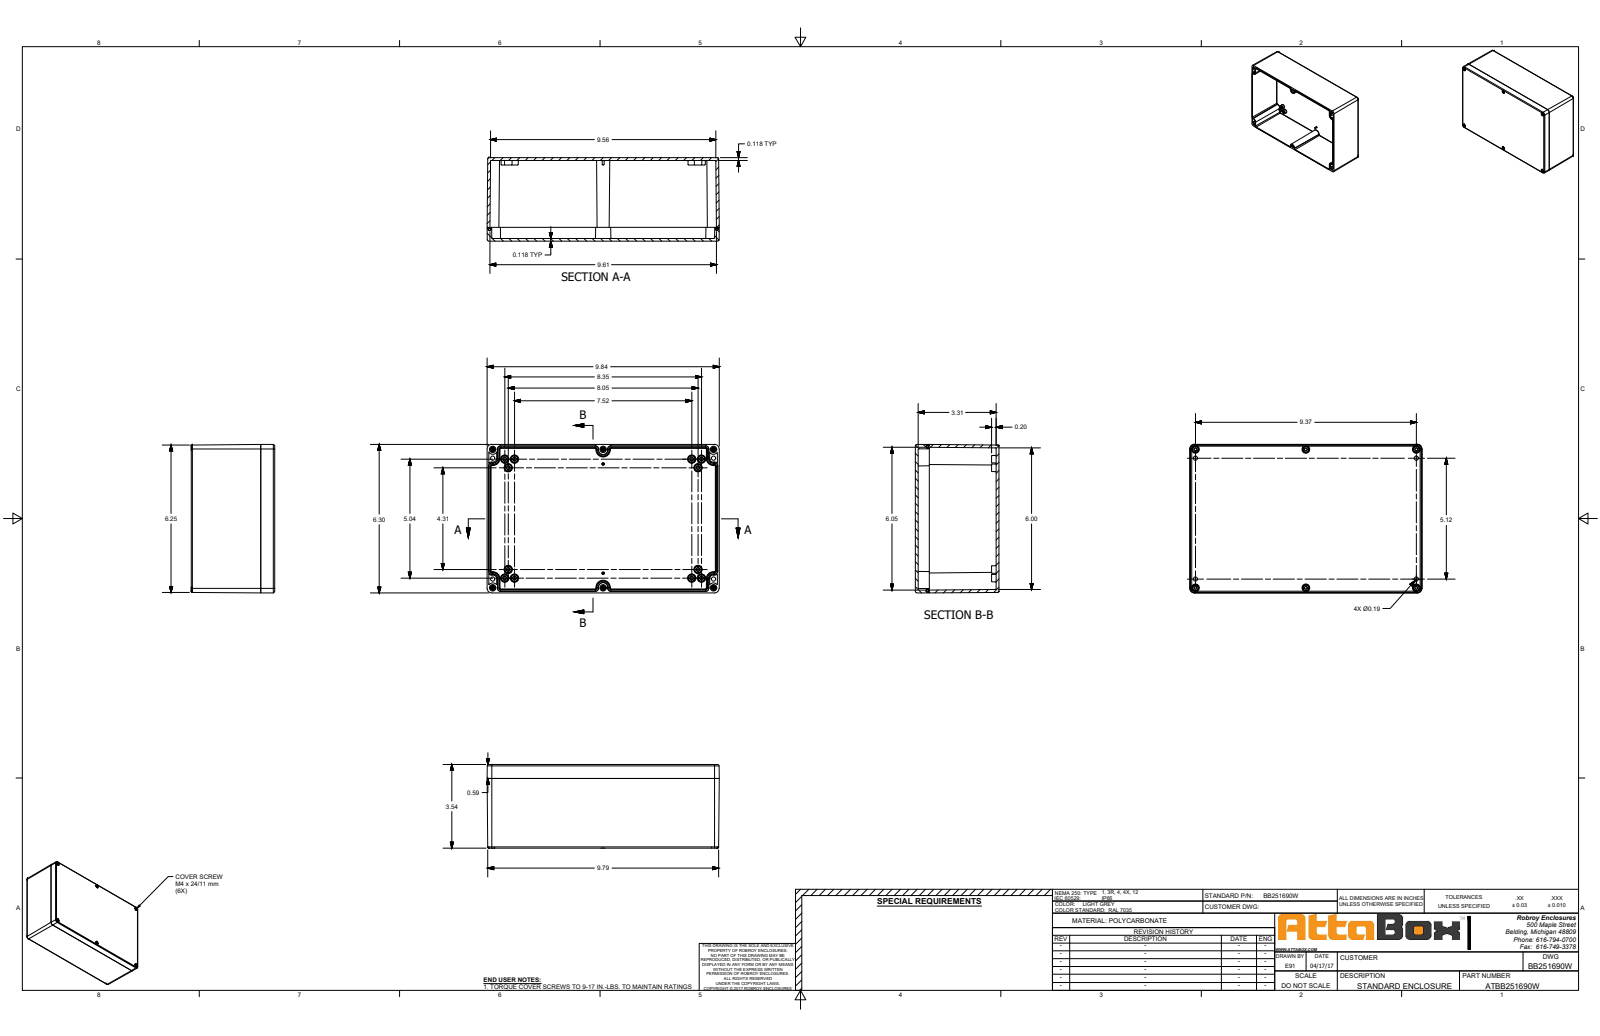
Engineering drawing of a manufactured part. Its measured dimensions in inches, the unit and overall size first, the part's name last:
Units: inches
Overall size (bounding box): 9.843 × 6.299 × 3.544
Round holes (diameter × count): ⌀0.128 ×6, ⌀0.177 ×6, ⌀0.193 ×6, ⌀0.201 ×6, ⌀0.276 ×6, ⌀0.291 ×6, ⌀0.323 ×6, ⌀0.185 ×4
Round bosses / shafts (diameter × count): ⌀0.268 ×6, ⌀0.173 ×6, ⌀0.157 ×6, ⌀0.13 ×6
Partial cylindrical surfaces — rounded edges, fillets, slot ends (radius × count): R0.049 ×40, R0.02 ×32, R0.039 ×20, R0.059 ×16, R0.167 ×16, R0.004 ×12, R0.102 ×6, R0.124 ×6
Main face-to-face distances: 0.118, 3.425, 3.543, 3.307, 0.124, 6.175, 6.299, 6.112, 0.187, 5.988
Hole centre spacings: 0.374, 4.685, 4.7, 5.492, 7.219, 7.507, 9.37, 9.378
Volume: 30.25 in³ · Surface area: 532.6 in²
Bodies: 15 solids, 2437 faces (893 planar, 630 cylindrical, 914 other)
Part name (STEP PRODUCT): BB251690W
STEP written by: SolidWorks 2018 (AUTOMOTIVE_DESIGN)
